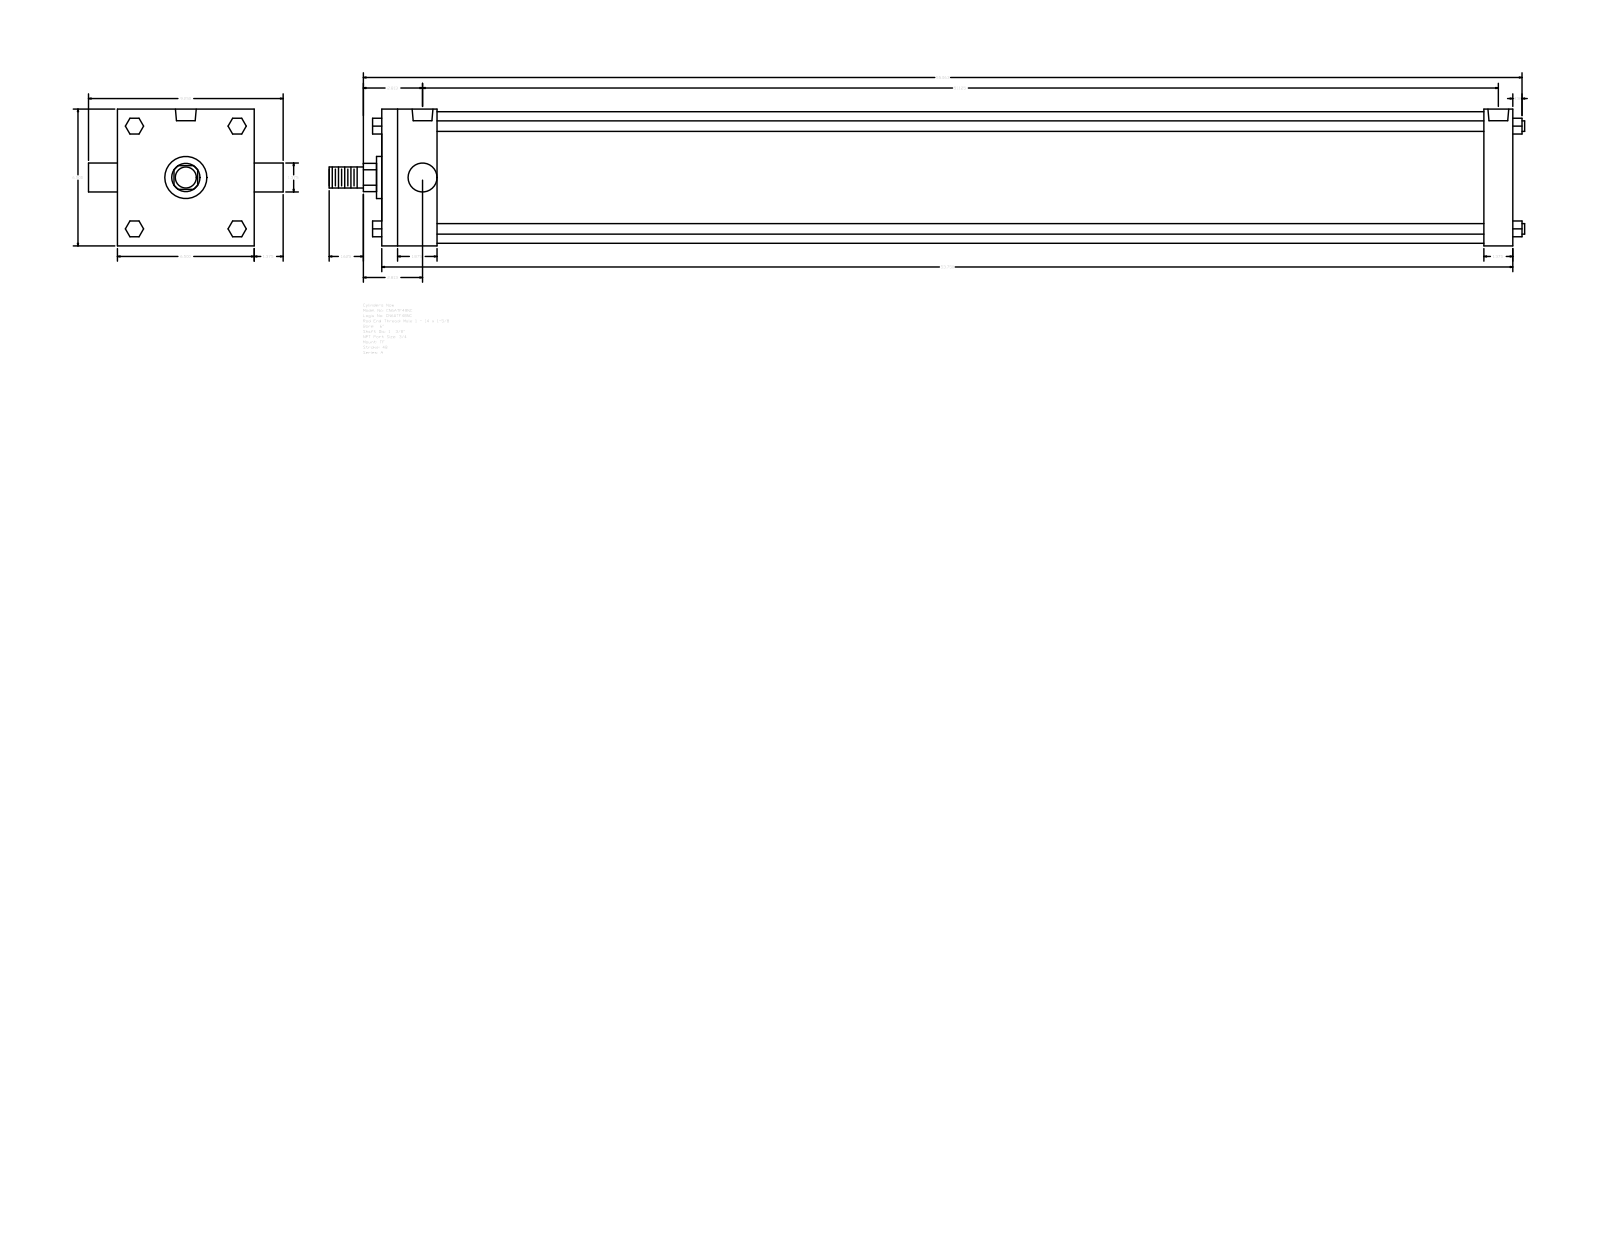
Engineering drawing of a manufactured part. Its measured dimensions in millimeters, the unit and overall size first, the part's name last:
Units: millimetres
Overall size (bounding box): 1443.04 × 234.95 × 165.1
Round holes (diameter × count): ⌀15.08 ×3, ⌀25.12 ×2
Round bosses / shafts (diameter × count): ⌀12.7 ×4, ⌀34.92 ×2, ⌀158.75 ×1, ⌀50.8 ×1, ⌀25.4 ×1
Partial cylindrical surfaces — rounded edges, fillets, slot ends (radius × count): R17.06 ×1
Main face-to-face distances: 165.1, 1365.24, 34.92, 66.67, 1298.57, 1330.32, 1263.65, 19.05, 61.97, 107.34
Hole centre spacings: 5.56, 1293.01, 1287.45, 1298.57
Bodies: 0 solids, 120 faces (92 planar, 28 cylindrical, 0 other)
Part name (STEP PRODUCT): A_TF__0600_1.375
STEP written by: GSSL Pune (CONFIG_CONTROL_DESIGN)
